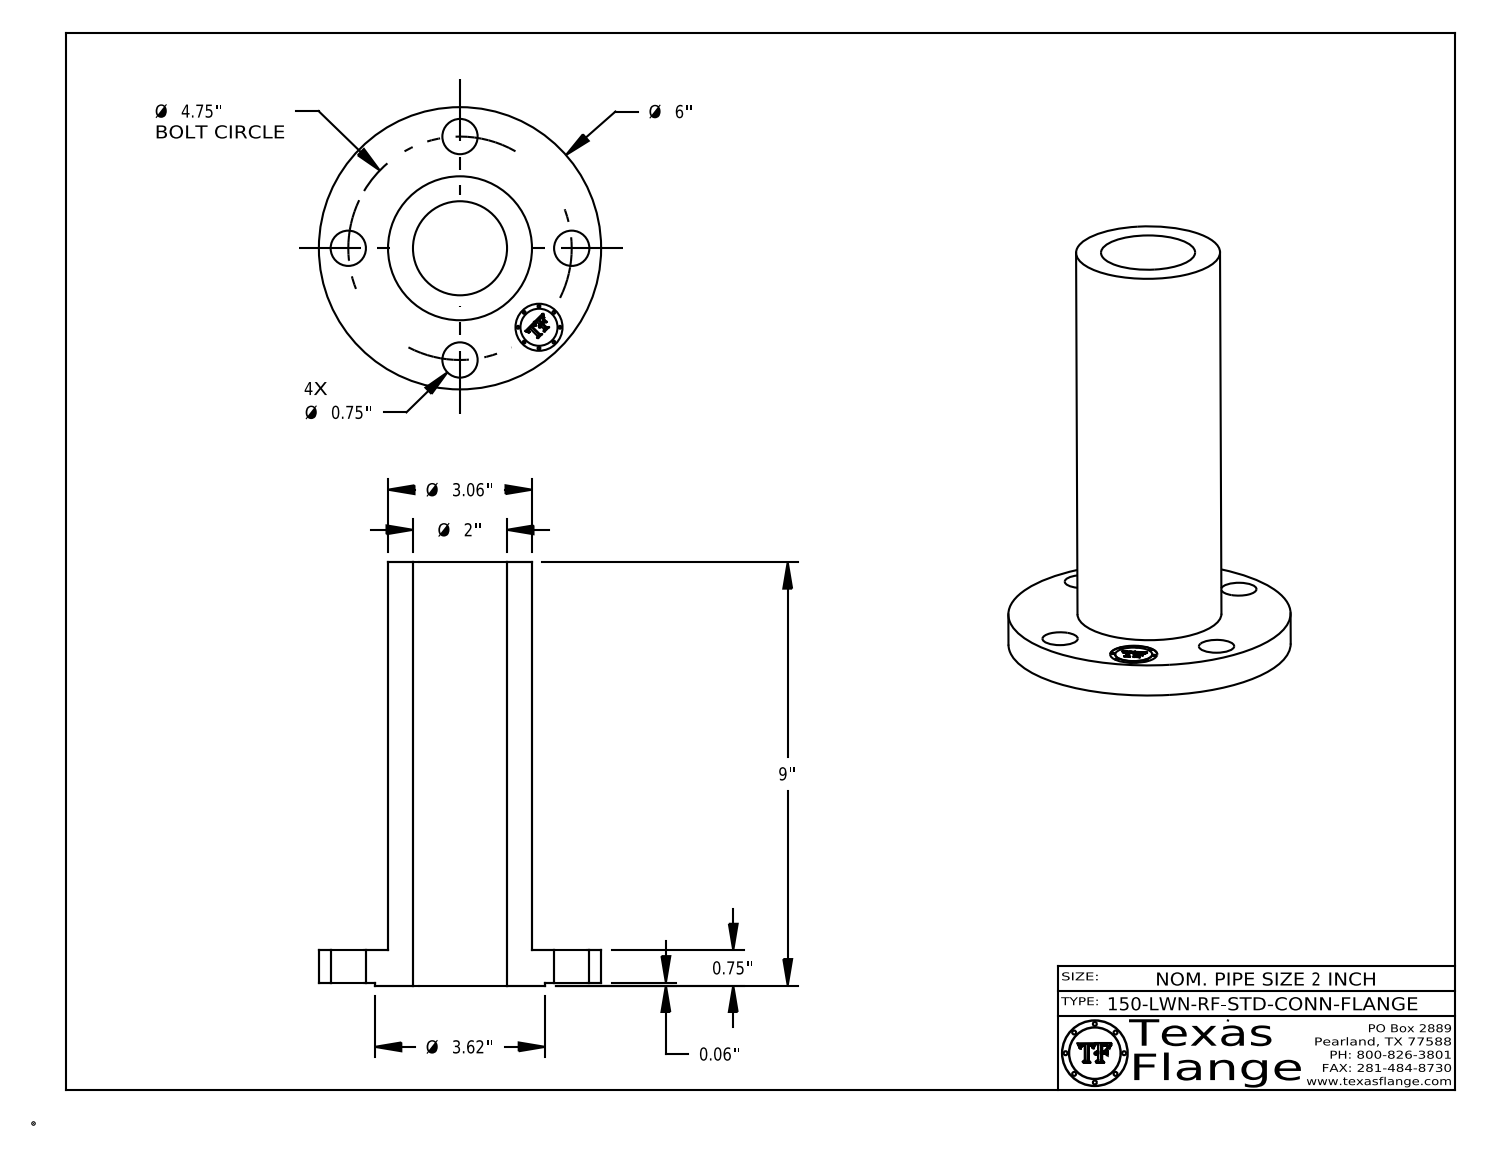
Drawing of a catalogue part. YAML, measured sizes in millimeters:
part_name: "2-150-LWN-RF-STD-CONN-FLANGE"
step_written_by: "CATIA V5 STEP AP214 (AUTOMOTIVE_DESIGN)"
units: millimeters
bodies: {solids: 1, faces: 405, planar: 369, cylindrical: 36, other: 0}
overall_size: [228.6, 152.4, 152.4]
volume: 840000
surface_area: 130800
round_holes:
  - {diameter: 19.1, count: 4}
  - {diameter: 25.4, count: 1}
  - {diameter: 50.8, count: 1}
round_bosses_or_shafts:
  - {diameter: 1.5, count: 8}
  - {diameter: 152.4, count: 1}
  - {diameter: 91.9, count: 1}
  - {diameter: 77.7, count: 1}
  - {diameter: 20, count: 1}
face_to_face_distances: [17.4, 1.6, 19.1, 228.6, 227, 209.6, 18.9, 17.3, 209.7, 7.6]
hole_center_spacings: [60.3, 85.3, 46.2, 111.5, 120.7]
